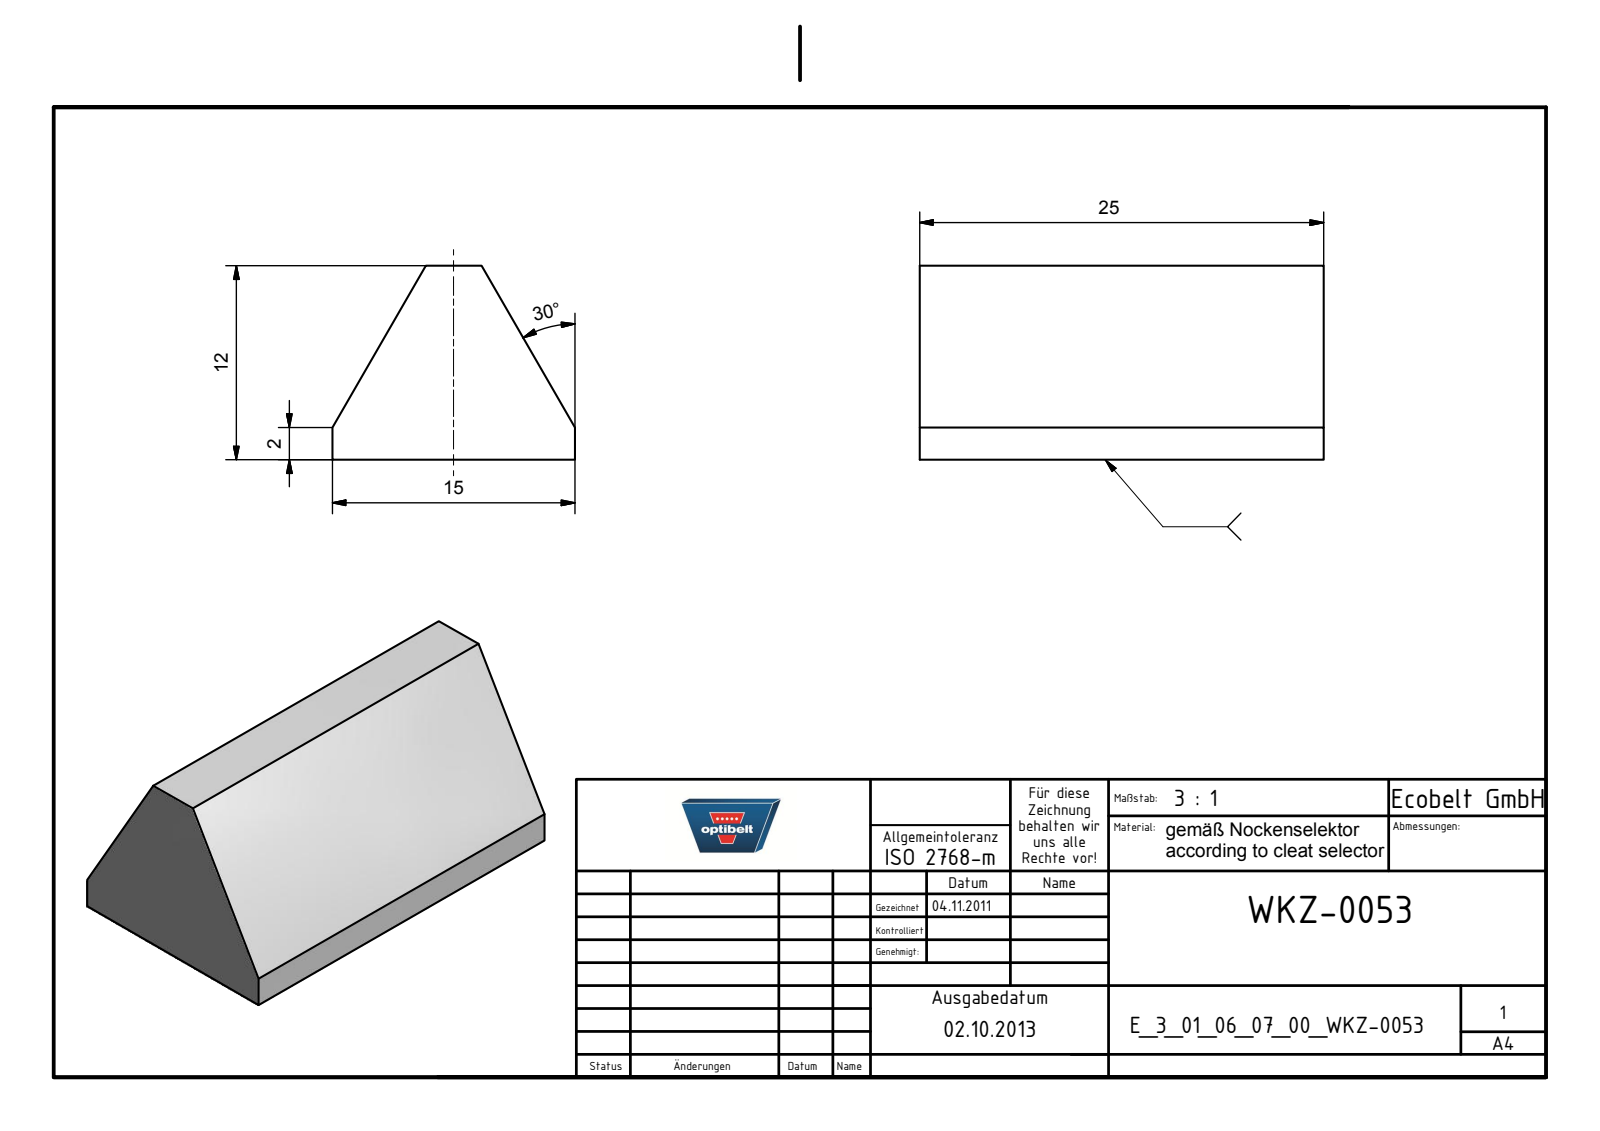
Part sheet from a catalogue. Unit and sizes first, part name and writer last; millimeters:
Units: millimetres
Overall size (bounding box): 25 × 15 × 12
Main face-to-face distances: 25, 12, 15
Volume: 3 057 mm³ · Surface area: 1 383 mm²
Bodies: 1 solid, 8 faces (8 planar, 0 cylindrical, 0 other)
Part name (STEP PRODUCT): E_3_01_06_07_00_WKZ-0053
STEP written by: Autodesk Inventor 2025 (AUTOMOTIVE_DESIGN)
